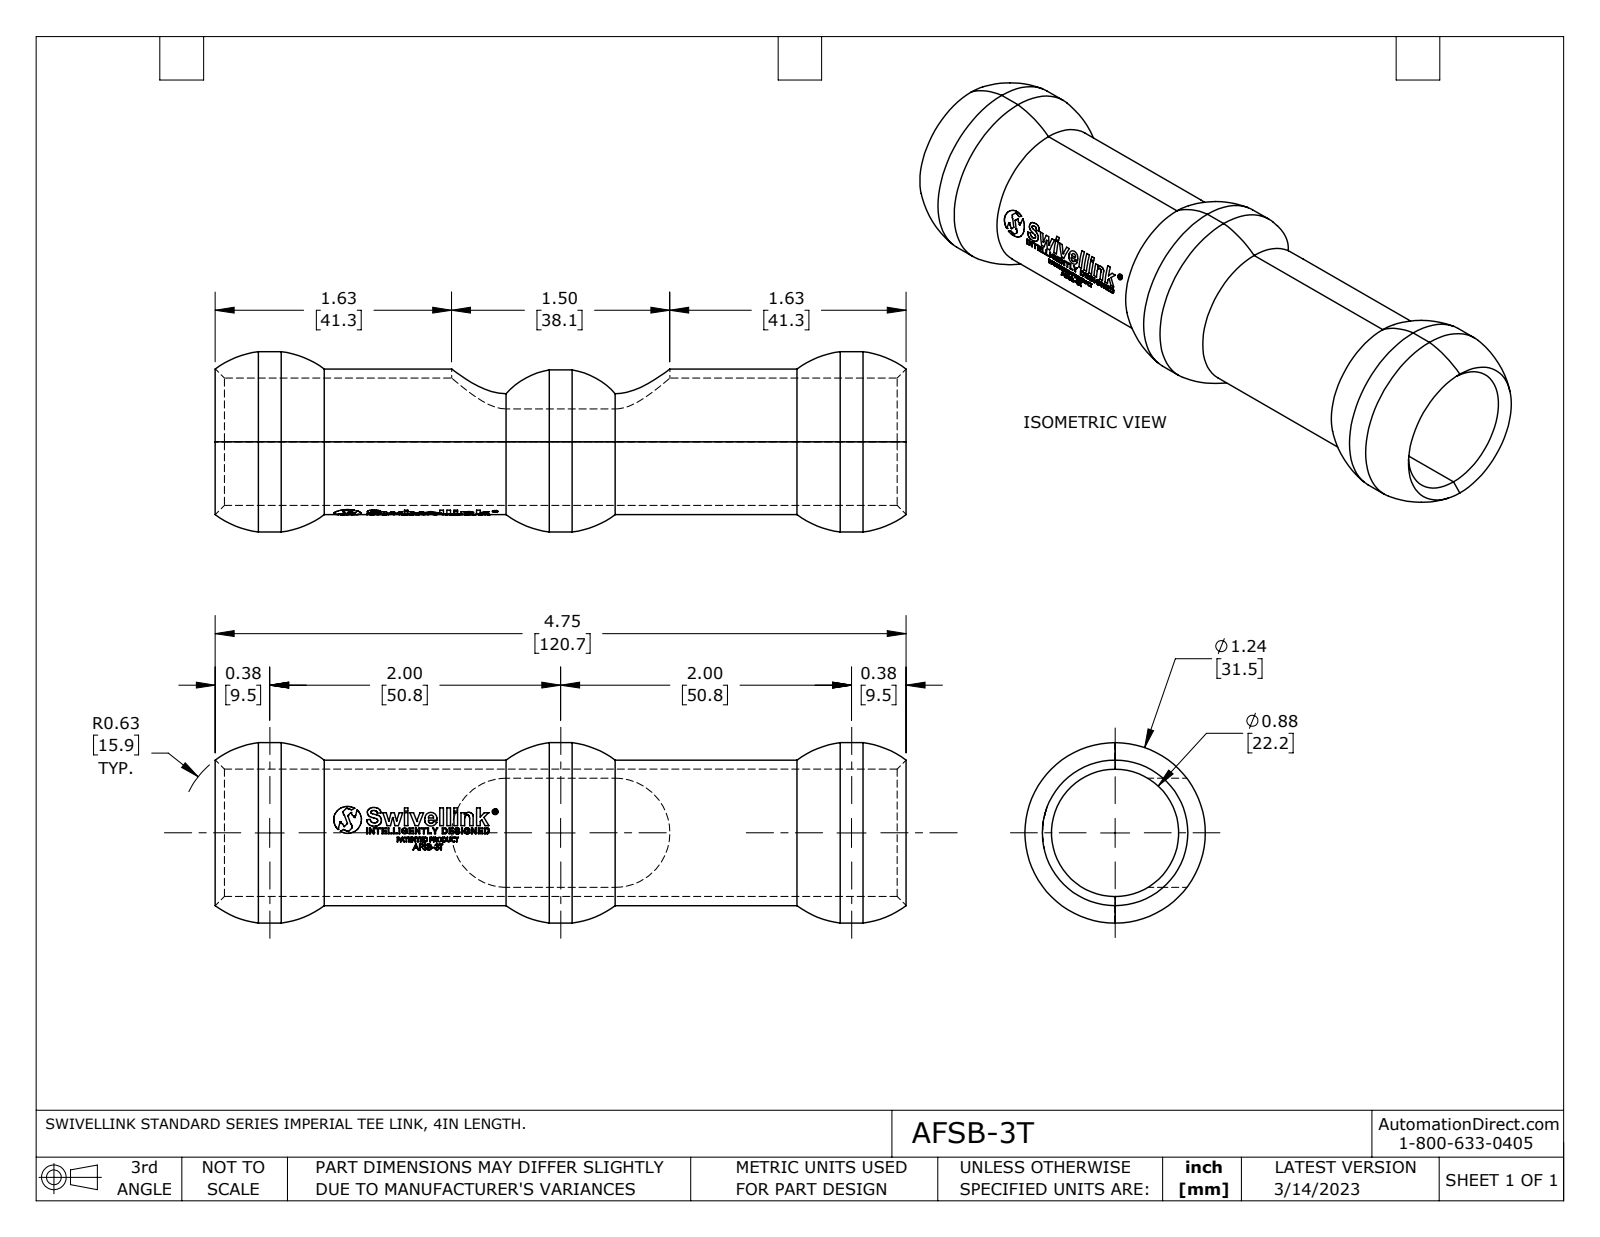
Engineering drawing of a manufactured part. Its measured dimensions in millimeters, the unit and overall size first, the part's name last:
Units: millimetres
Overall size (bounding box): 120.7 × 31.5 × 31.5
Round holes (diameter × count): ⌀22.2 ×1
Round bosses / shafts (diameter × count): ⌀31.5 ×1, ⌀25.4 ×1
Partial cylindrical surfaces — rounded edges, fillets, slot ends (radius × count): R9.5 ×2
Main face-to-face distances: 19.1
Volume: 22 860 mm³ · Surface area: 18 140 mm²
Bodies: 1 solid, 108 faces (2 planar, 88 cylindrical, 18 other)
Part name (STEP PRODUCT): AFSB-3T
STEP written by: SolidWorks 2021 (AUTOMOTIVE_DESIGN)
